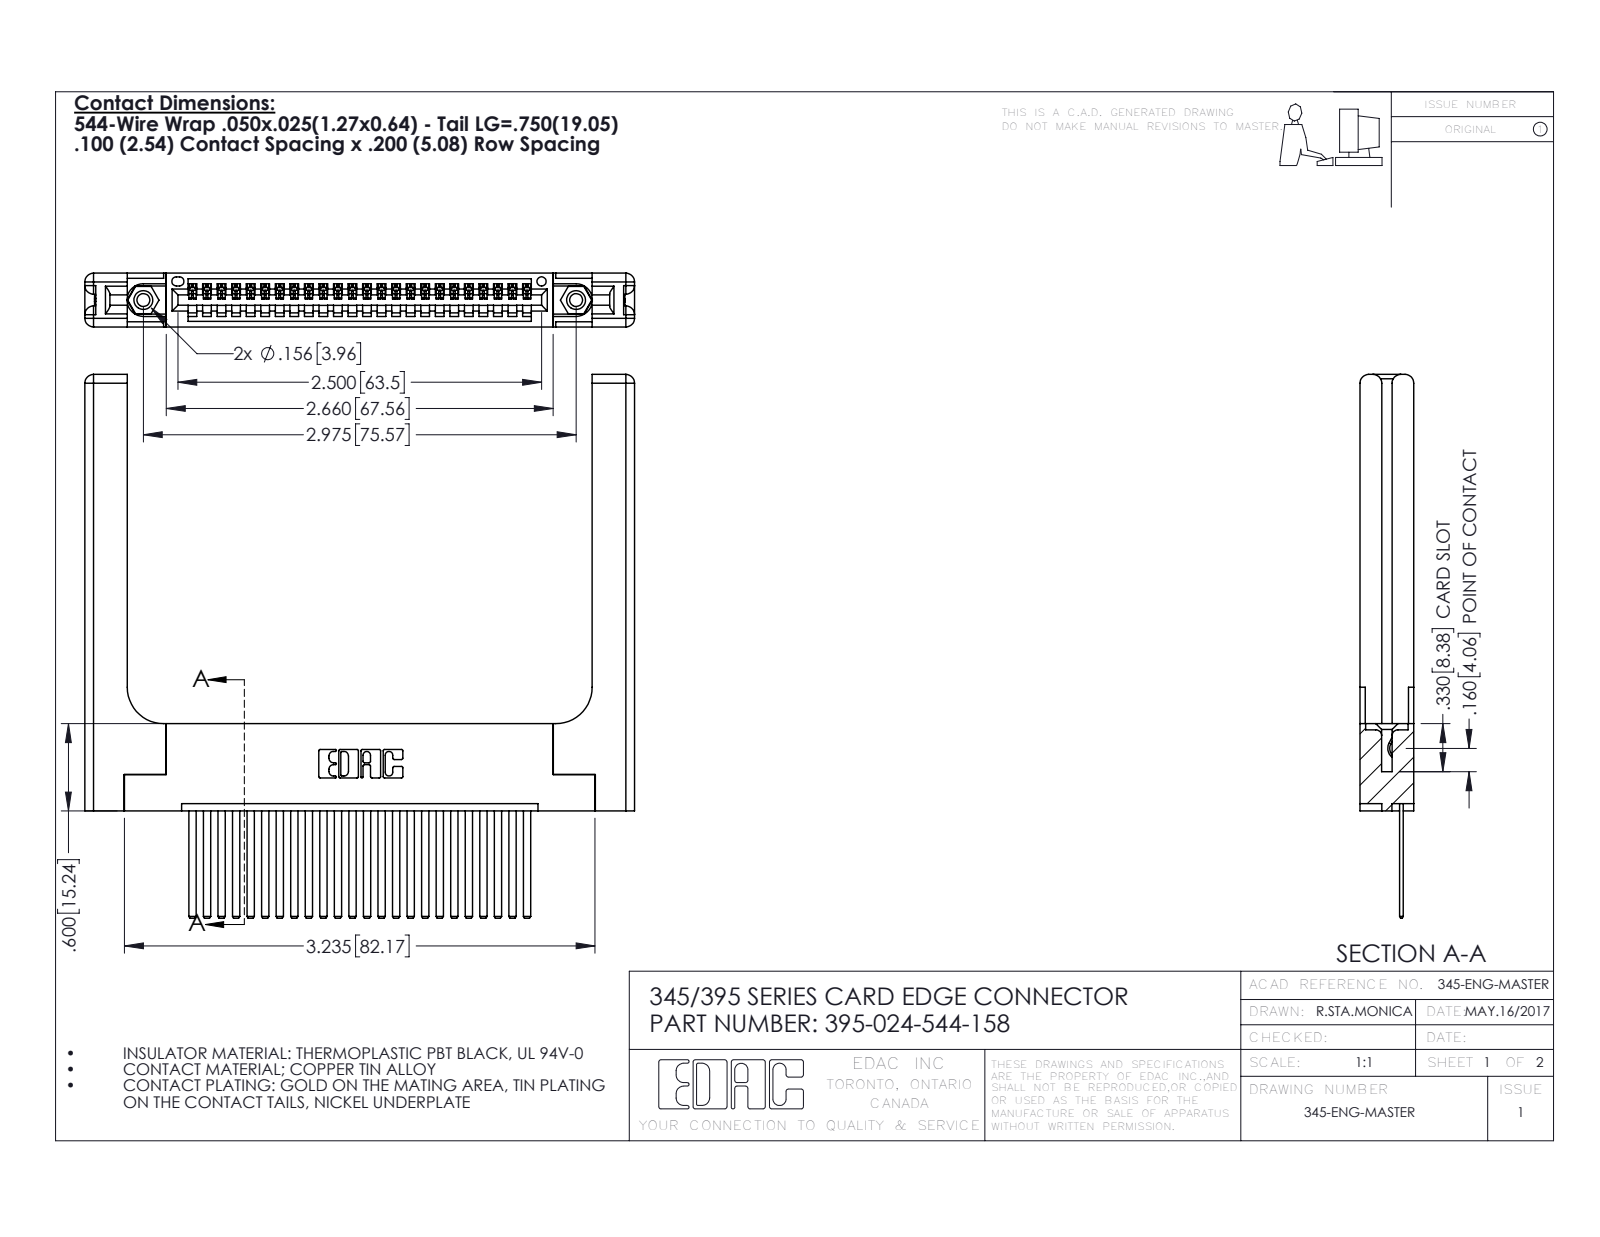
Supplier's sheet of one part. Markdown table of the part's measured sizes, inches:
| quantity | value |
| --- | --- |
| part name | 395-024-544-158; 345-220-058_345-220-058; 345-250-001_345-250-001-102; 345-292-001_345-293-144 (+1 more) |
| STEP written by | SolidWorks 2016 (CONFIG_CONTROL_DESIGN) |
| units | inches |
| bodies | 29 solids, 1630 faces (1092 planar, 478 cylindrical, 60 other) |
| overall size | 3.779 × 3.737 × 0.37 |
| volume | 1.083 in³ |
| surface area | 28.19 in² |
| round holes (diameter × count) | 0.089 × 2, 0.125 × 2, 0.156 × 2, 0.064 × 1 |
| round bosses / shafts (diameter × count) | 0.155 × 2 |
| partial cylindrical surfaces (radius × count) | 0.006 × 48, 0.01 × 22, 0.06 × 16, 0.007 × 6, 0.031 × 6, 0.026 × 3, 0.03 × 2, 0.031 × 2 |
| main face-to-face distances | 0.072, 0.37, 0.298, 0.098, 0.272, 0.025, 0.2, 0.148, 0.15, 0.077 |
| hole center spacings | 0.27, 2.741, 2.975 |
